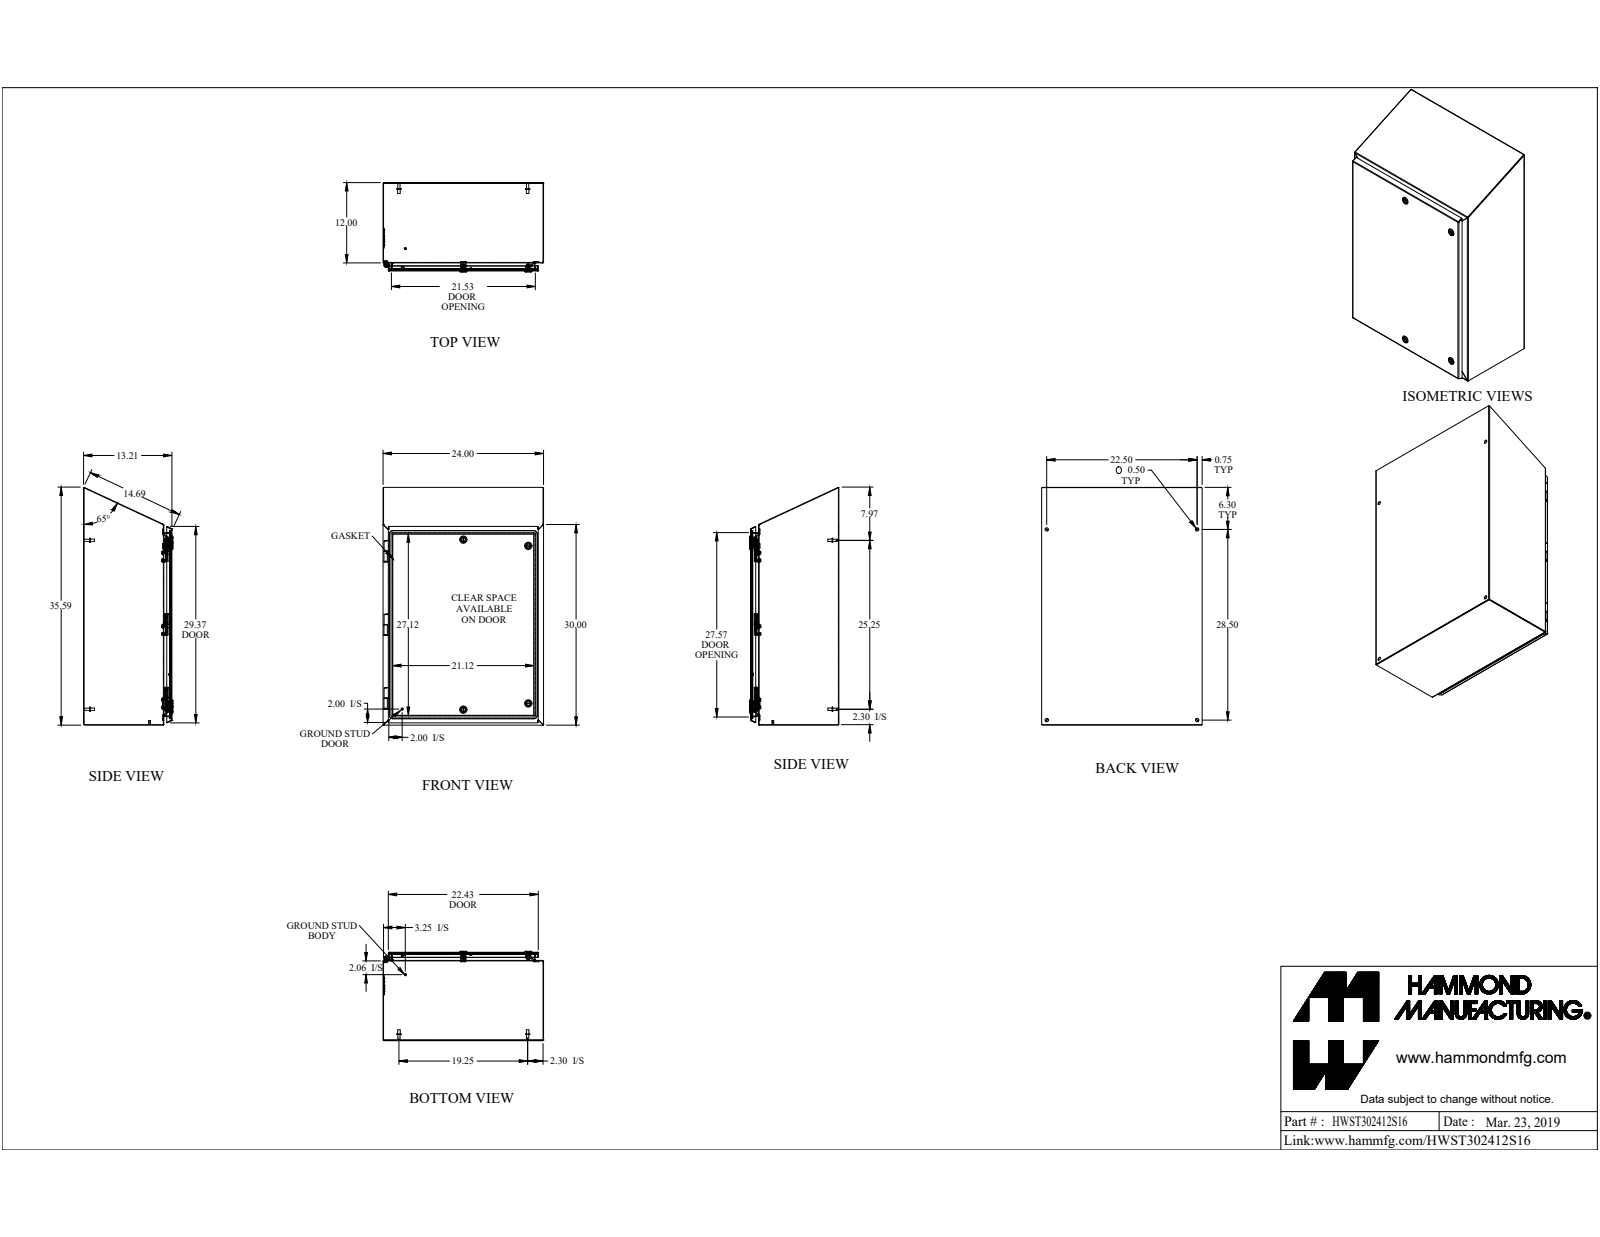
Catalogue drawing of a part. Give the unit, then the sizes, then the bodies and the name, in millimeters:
Units: millimetres
Overall size (bounding box): 902.8 × 609.6 × 339.6
Round holes (diameter × count): ⌀4.9 ×12, ⌀6.1 ×12, ⌀12.7 ×8, ⌀7 ×6, ⌀5 ×4, ⌀9.8 ×4, ⌀16 ×4, ⌀19.5 ×4, ⌀3.3 ×2, ⌀6.1 ×1, ⌀88.9 ×1
Round bosses / shafts (diameter × count): ⌀5.7 ×12, ⌀15.9 ×8, ⌀6 ×5, ⌀27.9 ×4, ⌀16.5 ×4, ⌀13.3 ×4, ⌀9.5 ×4, ⌀8.4 ×4
Partial cylindrical surfaces — rounded edges, fillets, slot ends (radius × count): R1 ×24, R6.4 ×24, R3.2 ×20, R0.9 ×18, R2.7 ×18, R0.3 ×16, R0.8 ×14, R3.4 ×6
Main face-to-face distances: 1.8, 607.8, 1.8, 331.9, 333.7, 333.7, 335.5, 605.9, 609.6, 303
Hole centre spacings: 29, 279.1, 279.1, 558.1, 29, 308.1, 247.9, 250.1
Volume: 4 139 000 mm³ · Surface area: 4 434 000 mm²
Bodies: 63 solids, 1510 faces (929 planar, 397 cylindrical, 184 other)
Part name (STEP PRODUCT): HWST302412S16
STEP written by: SolidWorks 2019 (AUTOMOTIVE_DESIGN)
